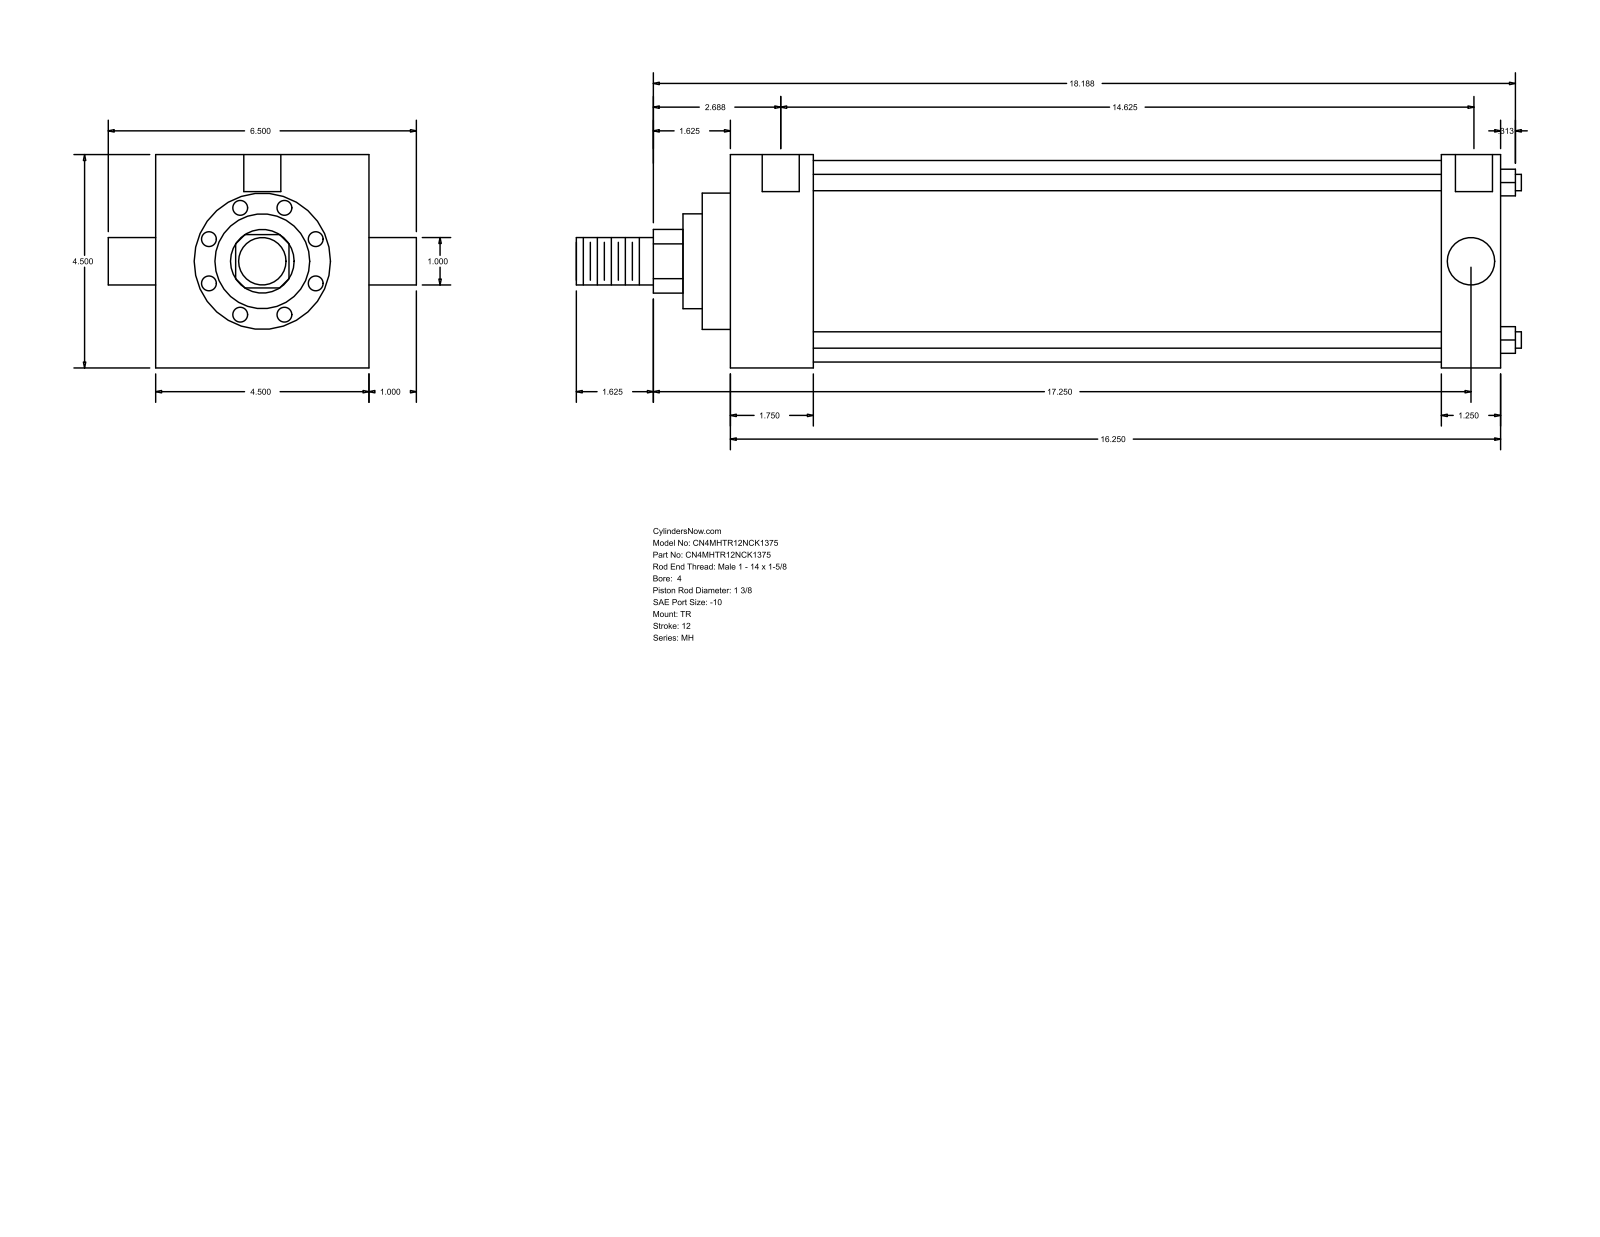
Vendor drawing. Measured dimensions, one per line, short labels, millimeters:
name: MH_TR__0400_1.375
written by: GSSL Pune (CONFIG_CONTROL_DESIGN)
unit: mm
bodies: 0 solids, 86 faces (61 planar, 25 cylindrical, 0 other)
size: 506.41 × 165.1 × 114.3
holes: 3× ⌀8.73, 2× ⌀19.84
bosses: 4× ⌀8.76, 2× ⌀25.4, 1× ⌀107.95, 1× ⌀73.03, 1× ⌀50.8, 1× ⌀34.92
rounds: 1× R17.06
face distances: 114.3, 412.75, 44.45, 368.3, 381, 336.55, 31.75, 15.08, 59.53, 396.08
hole spacings: 1.58, 1.59, 371.48, 373.06, 373.07, 374.65
